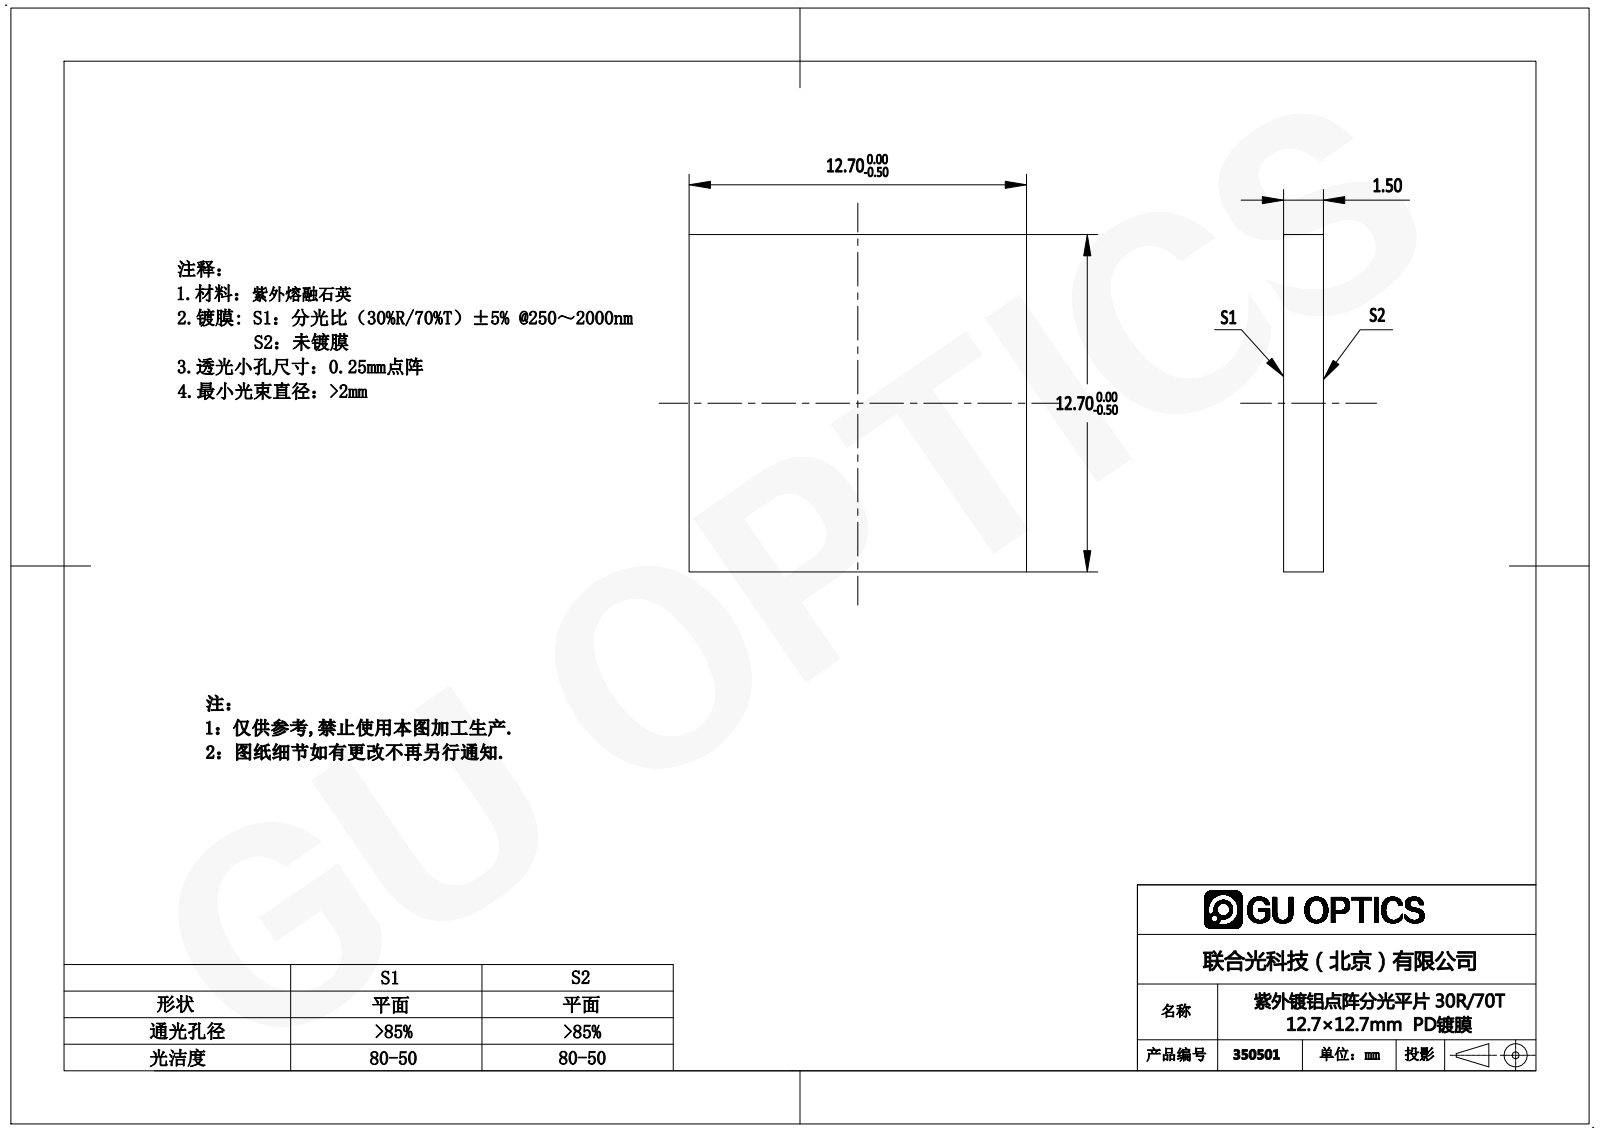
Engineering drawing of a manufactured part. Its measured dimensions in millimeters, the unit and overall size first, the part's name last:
Units: millimetres
Overall size (bounding box): 12.7 × 12.7 × 1.5
Main face-to-face distances: 1.5, 12.7
Volume: 242 mm³ · Surface area: 399 mm²
Bodies: 1 solid, 6 faces (6 planar, 0 cylindrical, 0 other)
Part name (STEP PRODUCT): 350501
STEP written by: SolidWorks 2016 (AUTOMOTIVE_DESIGN)
